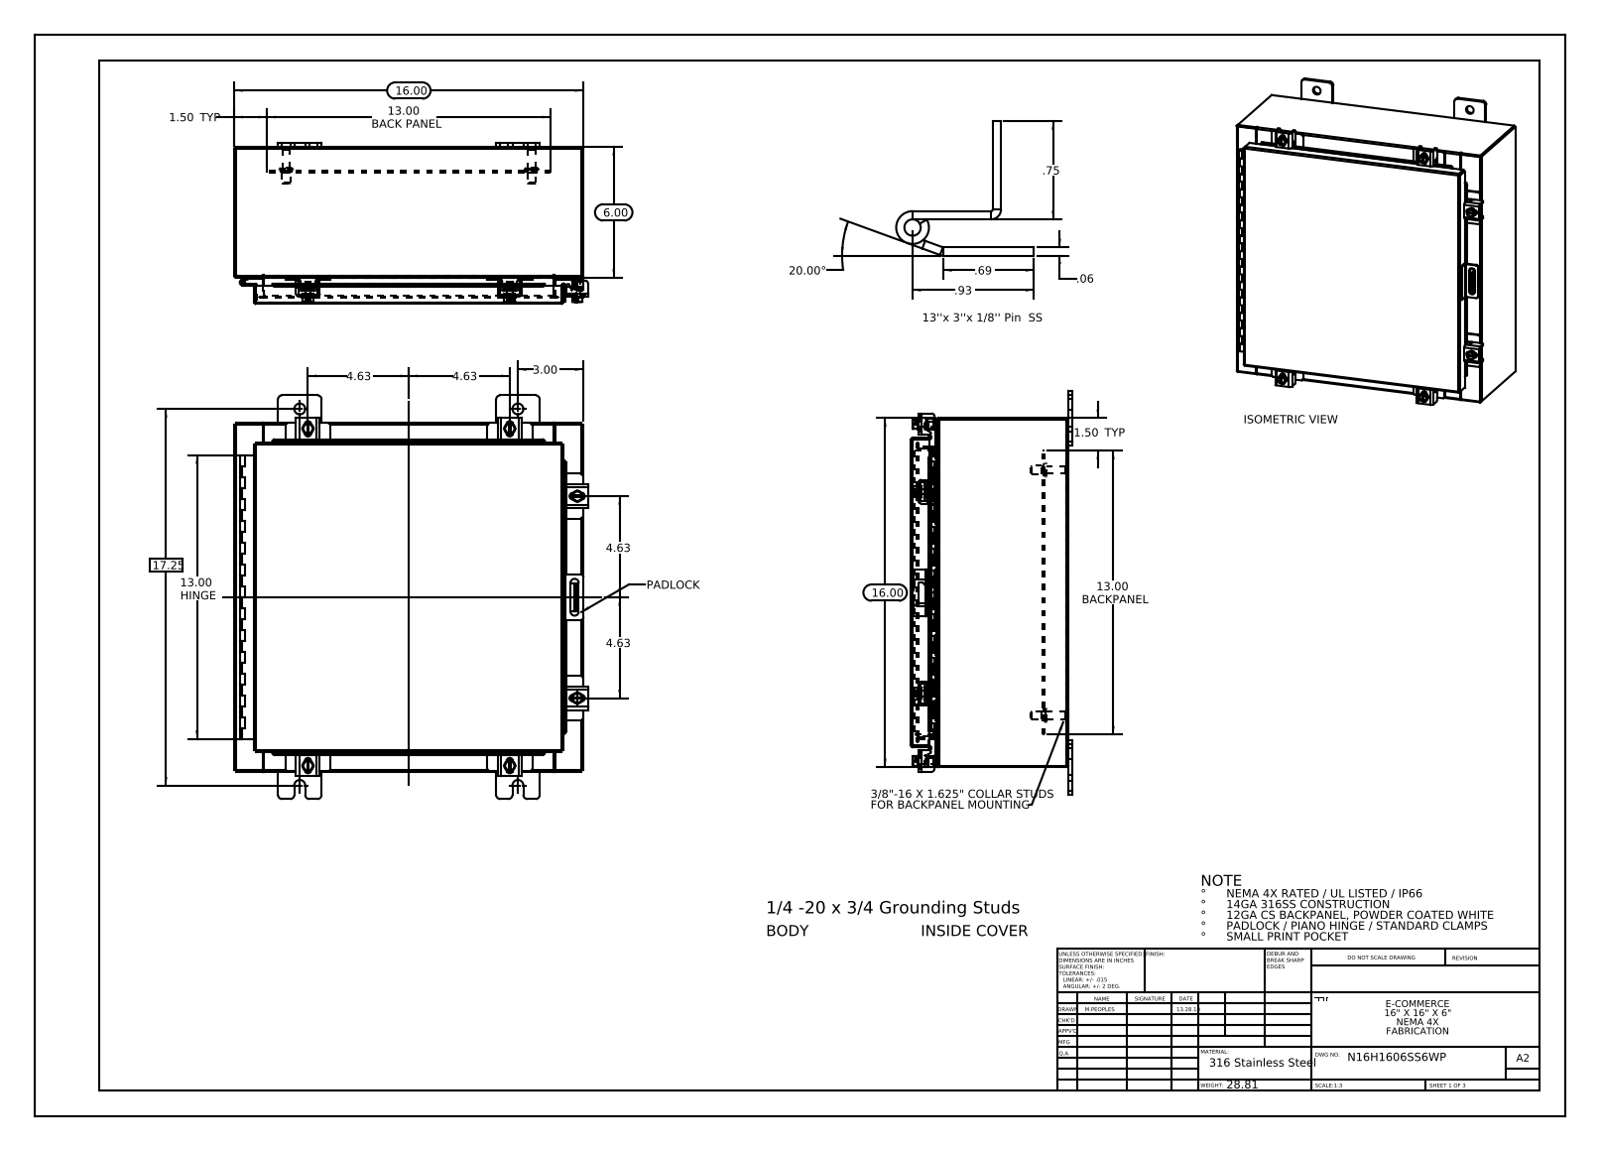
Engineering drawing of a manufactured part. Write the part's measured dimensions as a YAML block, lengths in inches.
part_name: "N16H1606SS6WP Padlock Hasp; N16H1606SS6WP Backpanel; N16H1606SS6WP Clamp Assembly; N16H1606SS6WP Clamp Bracket (+8 more)"
step_written_by: "SolidWorks 2013 (CONFIG_CONTROL_DESIGN)"
units: inches
bodies: {solids: 47, faces: 1501, planar: 800, cylindrical: 605, other: 96}
overall_size: [18.5, 16.211, 7.389]
volume: 102.2
surface_area: 2591
round_holes:
  - {diameter: 0.5, count: 8}
  - {diameter: 0.213, count: 6}
  - {diameter: 0.26, count: 6}
  - {diameter: 0.125, count: 2}
  - {diameter: 0.125, count: 1}
round_bosses_or_shafts:
  - {diameter: 0.25, count: 7}
  - {diameter: 0.5, count: 6}
  - {diameter: 0.399, count: 6}
  - {diameter: 0.625, count: 4}
  - {diameter: 0.375, count: 4}
  - {diameter: 0.33, count: 4}
partial_cylinders:
  - {radius: 0.06, count: 30}
  - {radius: 0.19, count: 24}
  - {radius: 0.013, count: 23}
  - {radius: 0.088, count: 21}
  - {radius: 0.12, count: 12}
  - {radius: 0.141, count: 12}
  - {radius: 0.125, count: 10}
  - {radius: 0.05, count: 9}
face_to_face_distances: [0.075, 7.126, 15.925, 7.201, 7.051, 15.85, 16, 1, 1.075, 6.051]
hole_center_spacings: [13.388, 10.463, 16.832, 1.858, 2.326, 2.326, 2.327, 3.065]
